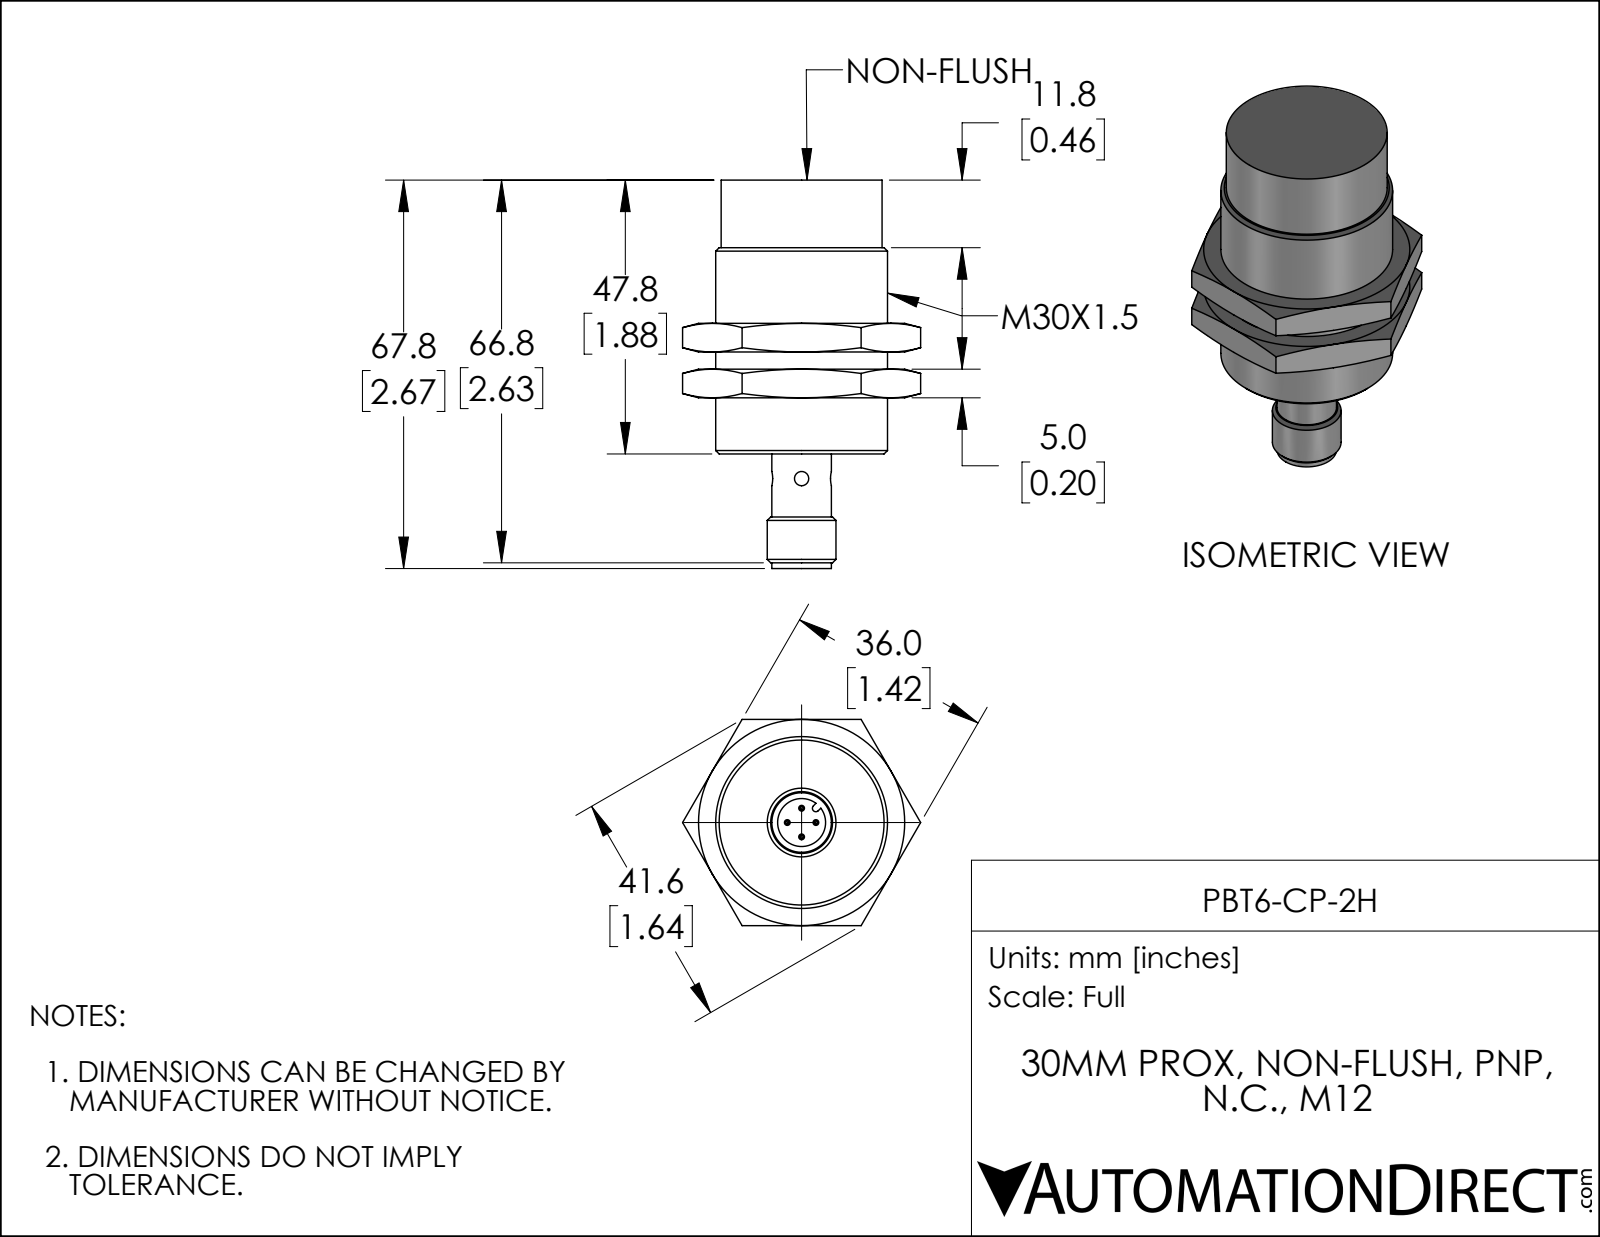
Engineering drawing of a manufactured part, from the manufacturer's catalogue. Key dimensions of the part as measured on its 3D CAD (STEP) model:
Part name (STEP PRODUCT): DSD-0303
STEP written by: SolidWorks 2019 (AUTOMOTIVE_DESIGN)
Units: inches
Bodies: 1 solid, 40 faces (17 planar, 15 cylindrical, 8 other)
Overall size (bounding box): 2.669 × 1.181 × 1.181
Volume: 2.085 in³ · Surface area: 10.64 in²
Round holes (diameter × count): ⌀0.098 ×2, ⌀0.33 ×1
Round bosses / shafts (diameter × count): ⌀0.039 ×4, ⌀1.181 ×1, ⌀1.106 ×1, ⌀0.472 ×1, ⌀0.409 ×1
Partial cylindrical surfaces — rounded edges, fillets, slot ends (radius × count): R0.024 ×1
Main face-to-face distances: 1.882, 2.319, 0.437, 0.465, 1.417, 1.854, 2.669, 2.205, 0.787, 0.35
